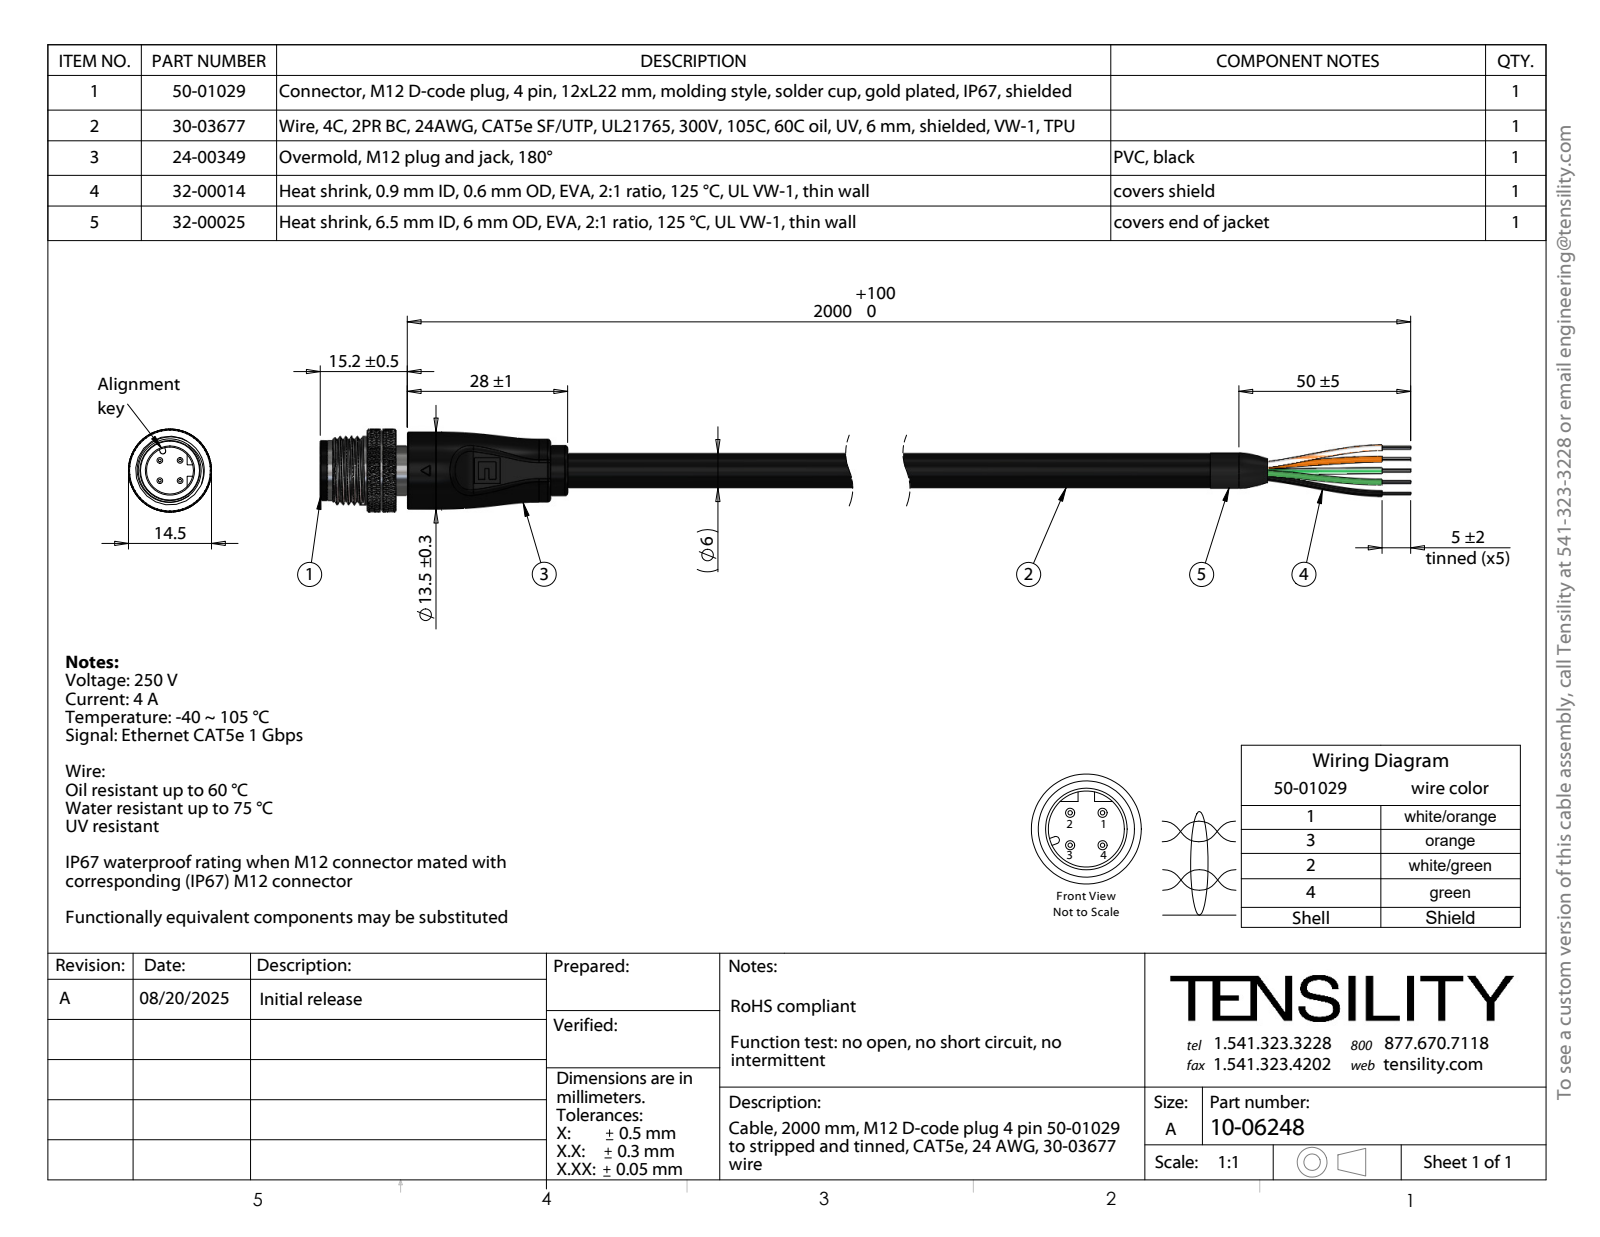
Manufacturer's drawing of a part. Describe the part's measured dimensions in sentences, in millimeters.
The part is named "50-01029-02_默认; 30-03677_s + t; 50-01029-04_默认; 50-01029-01_默认 (+4 more)". Its 3-D file was written by "SolidWorks 2025 (CONFIG_CONTROL_DESIGN)". It is 86 solids with 2792 faces: 263 planar, 823 cylindrical and 1706 other. Overall it measures 223.2 by 14.5 by 14.5 millimeters. Its volume is 9 287 cubic millimeters and its surface area 26 453 square millimeters. Round holes: 28 of diameter 0.2, 4 of diameter 1, 4 of diameter 1.05, 1 of diameter 3.16, 1 of diameter 3.21, 1 of diameter 3.36, 1 of diameter 8, 1 of diameter 8.2, 1 of diameter 8.8, 1 of diameter 9.5. Round bosses or shafts: 35 of diameter 0.2, 4 of diameter 1.4, 1 of diameter 14.5, 1 of diameter 13.9, 1 of diameter 13.5, 1 of diameter 12, 1 of diameter 11, 1 of diameter 10.5. Partial cylindrical surfaces (rounded edges, fillets, slot ends): 2 of radius 0.5, 2 of radius 1.5, 2 of radius 1.96, 1 of radius 5, 1 of radius 5.58, 1 of radius 6.75. The main face-to-face distances are 180, 7, 2, 178, 5, 28, 30, 150, 10.8, 3.8. The hole center spacings are 1.91, 2.09, 1.06, 0.35, 0.89, 1.08, 1.24, 1.71.
